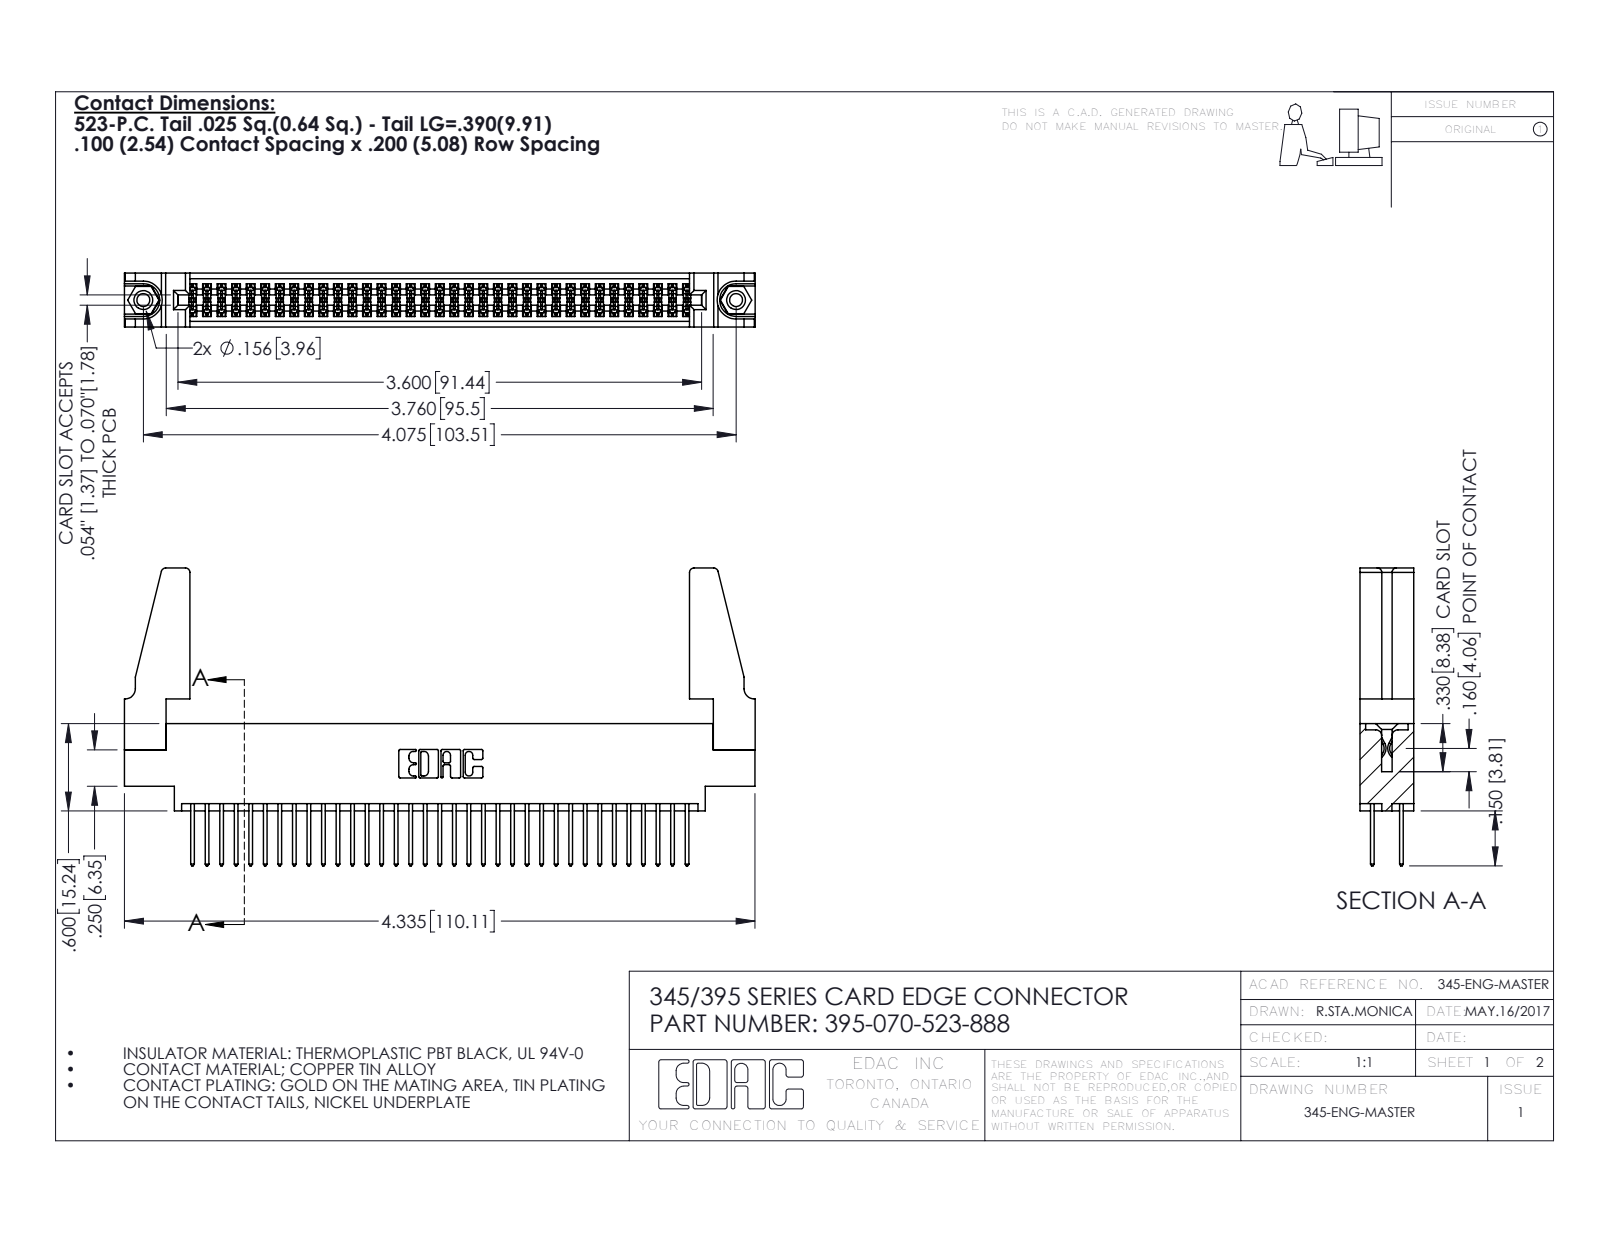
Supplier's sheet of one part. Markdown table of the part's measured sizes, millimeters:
| quantity | value |
| --- | --- |
| part name | 345 Part_0.170 Offset - 0.156 Dia-TH; 345-220-078_345-220-088; 395-070-523-888; 345-292-001_345-293-123 (+1 more) |
| STEP written by | SolidWorks 2016 (CONFIG_CONTROL_DESIGN) |
| units | millimeters |
| bodies | 75 solids, 3754 faces (2466 planar, 1272 cylindrical, 16 other) |
| overall size | 110.1 × 52 × 9.4 |
| volume | 13 900 mm³ |
| surface area | 19 540 mm² |
| round holes (diameter × count) | 2.3 × 2, 3.2 × 2, 4 × 2, 1.6 × 1 |
| round bosses / shafts (diameter × count) | 3.9 × 2 |
| partial cylindrical surfaces (radius × count) | 0.2 × 105, 0.3 × 70, 0.3 × 22, 0.8 × 8, 0.2 × 6, 0.8 × 6, 0.7 × 3, 0.4 × 2 |
| main face-to-face distances | 1.8, 7.6, 9.4, 2.5, 6.9, 0.6, 5.1, 5.7, 4.4, 3.8 |
| hole center spacings | 6.9, 97.5, 103.5 |
